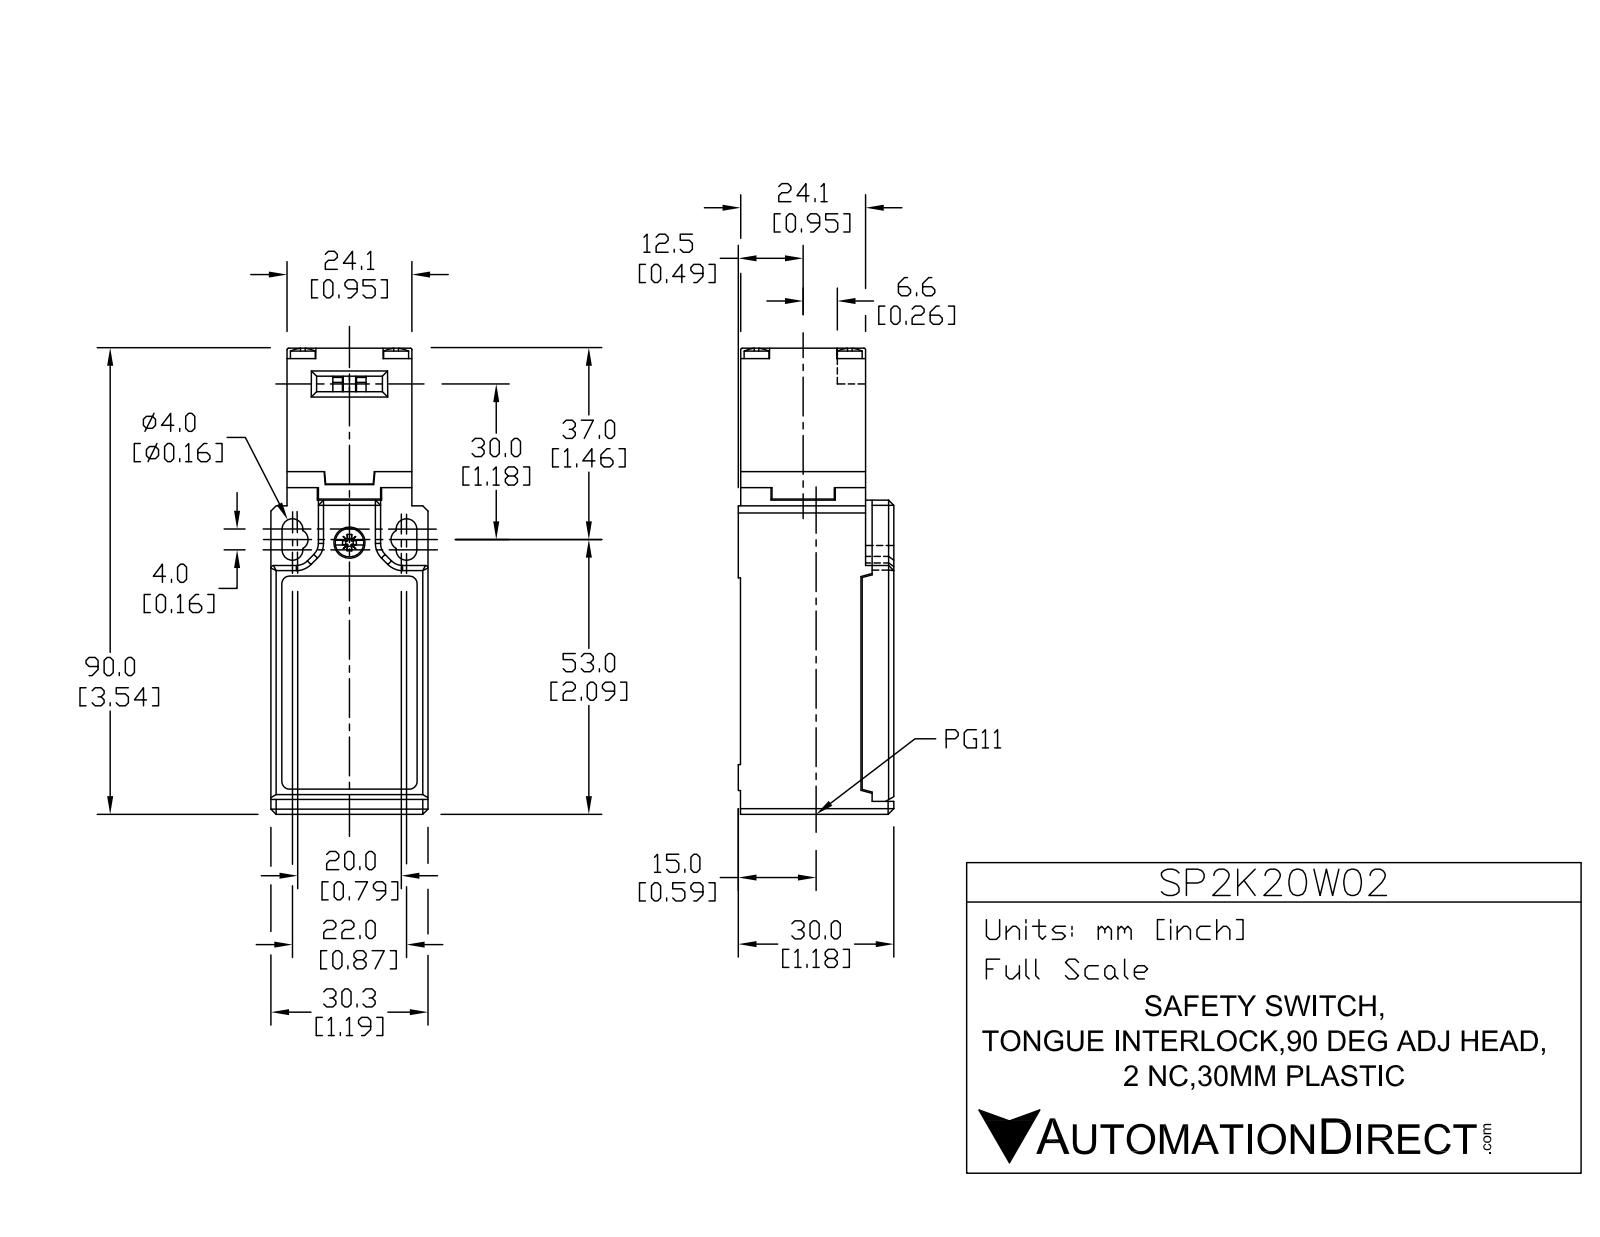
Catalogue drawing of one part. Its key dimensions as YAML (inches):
part_name: "SP2K20W02"
step_written_by: "SolidWorks 2017 (AUTOMOTIVE_DESIGN)"
units: inches
bodies: {solids: 2, faces: 167, planar: 112, cylindrical: 44, other: 11}
overall_size: [3.555, 1.204, 1.193]
volume: 4.001
surface_area: 24.3
round_holes:
  - {diameter: 0.236, count: 1}
  - {diameter: 0.669, count: 1}
  - {diameter: 0.748, count: 1}
round_bosses_or_shafts:
  - {diameter: 0.189, count: 4}
  - {diameter: 0.22, count: 1}
partial_cylinders:
  - {radius: 0.079, count: 6}
  - {radius: 0.012, count: 4}
  - {radius: 0.098, count: 4}
  - {radius: 0.118, count: 4}
  - {radius: 0.394, count: 1}
  - {radius: 0.4, count: 1}
face_to_face_distances: [1.193, 0.945, 1.165, 0.124, 1.069, 0.22, 2.406, 1.181, 0.961, 0.016]
